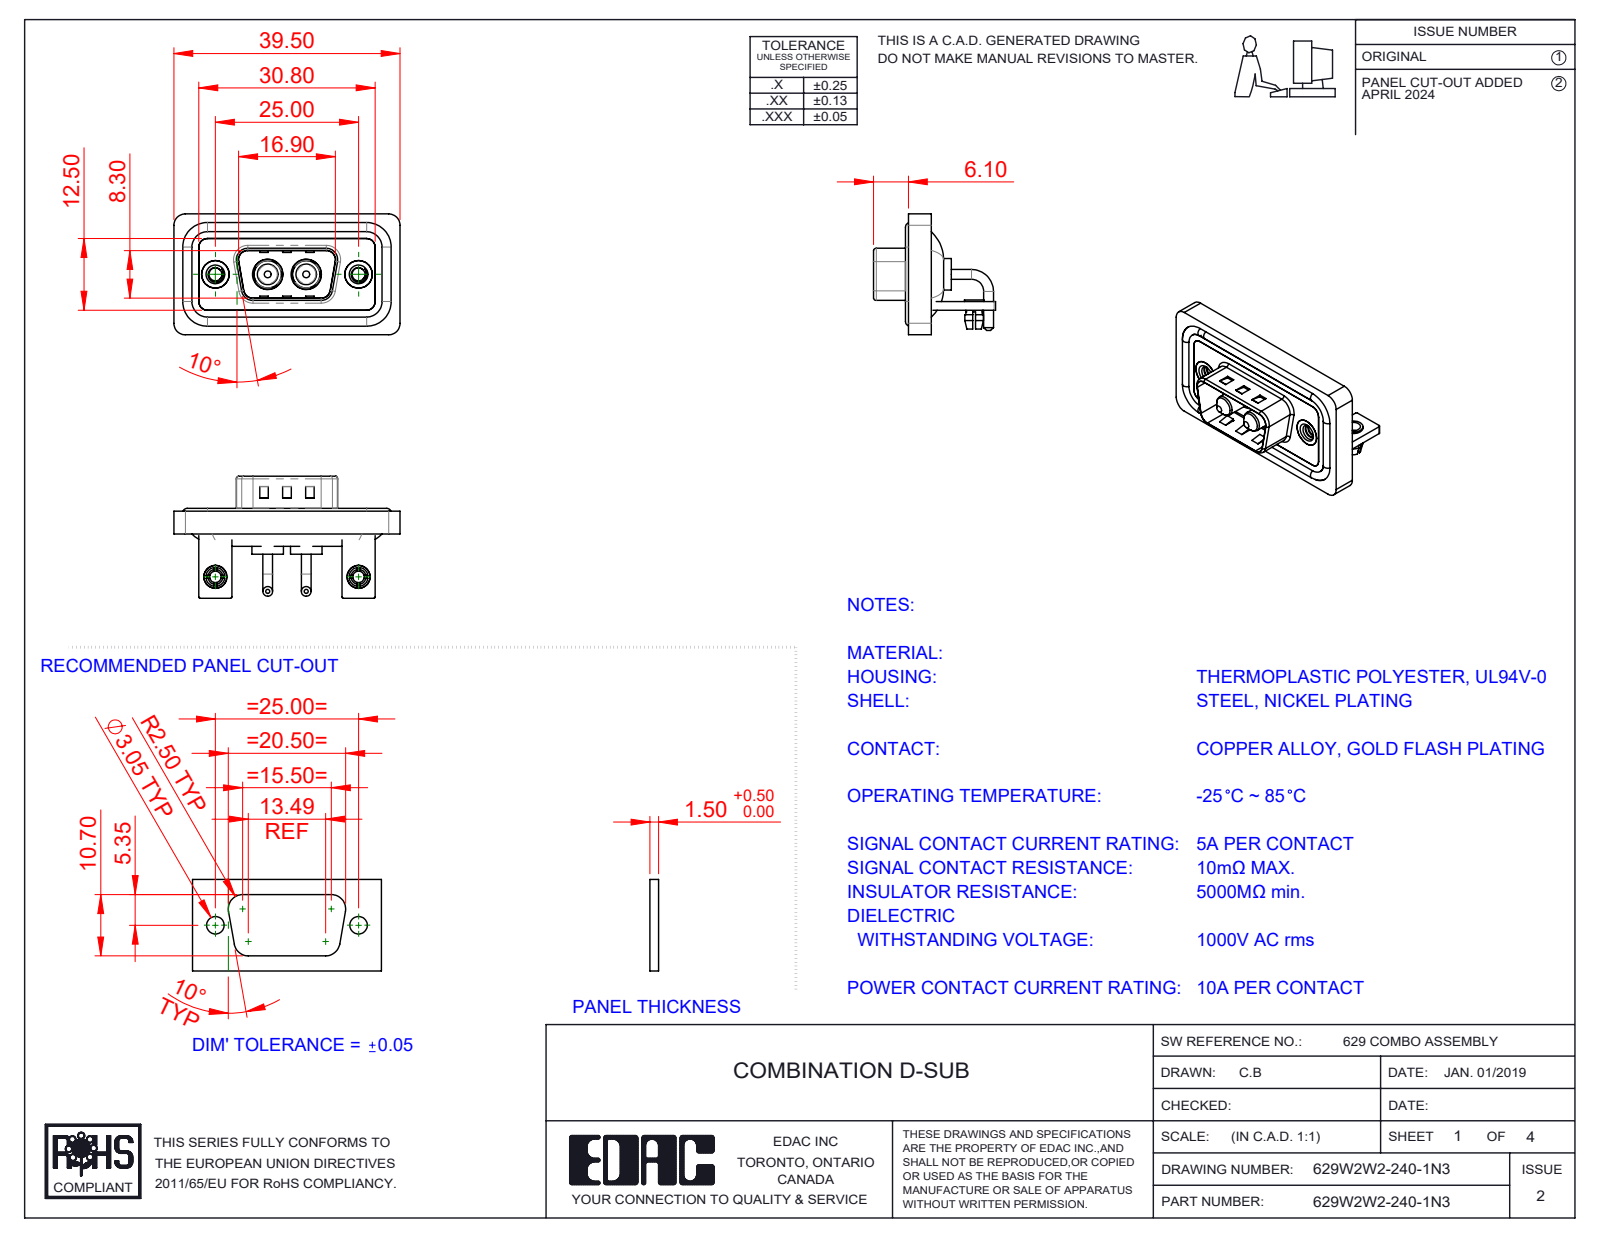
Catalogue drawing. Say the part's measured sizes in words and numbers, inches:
The part is named "629Combo Threaded Rivet_3; 629Combo Housing_2W2; 629W2W2-240-1N3; 629Combo Stabilizer Bracket (+5 more)". Its 3-D file was written by "SolidWorks 2023 (CONFIG_CONTROL_DESIGN)". It is 15 solids with 629 faces: 233 planar, 272 cylindrical and 124 other. Overall it measures 1.555 by 0.839 by 0.831 inches. Its volume is 0.292 cubic inches and its surface area 12.19 square inches. Round holes: 2 of diameter 0.079, 2 of diameter 0.089, 2 of diameter 0.098, 2 of diameter 0.126, 2 of diameter 0.157, 2 of diameter 0.189, 2 of diameter 0.191, 2 of diameter 0.197, 2 of diameter 0.209. Round bosses or shafts: 4 of diameter 0.067, 4 of diameter 0.063, 2 of diameter 0.217, 2 of diameter 0.205, 2 of diameter 0.193, 2 of diameter 0.187, 2 of diameter 0.157, 2 of diameter 0.148. Partial cylindrical surfaces (rounded edges, fillets, slot ends): 19 of radius 0.079, 18 of radius 0.059, 16 of radius 0.01, 9 of radius 0.02, 8 of radius 0.063, 4 of radius 0.024, 4 of radius 0.026, 4 of radius 0.035. The main face-to-face distances are 0.016, 0.059, 0.114, 0.031, 0.043, 0.047, 0.083, 0.063, 0.146, 0.098. The hole center spacings are 0.36, 0.624, 0.984, 0.265.
